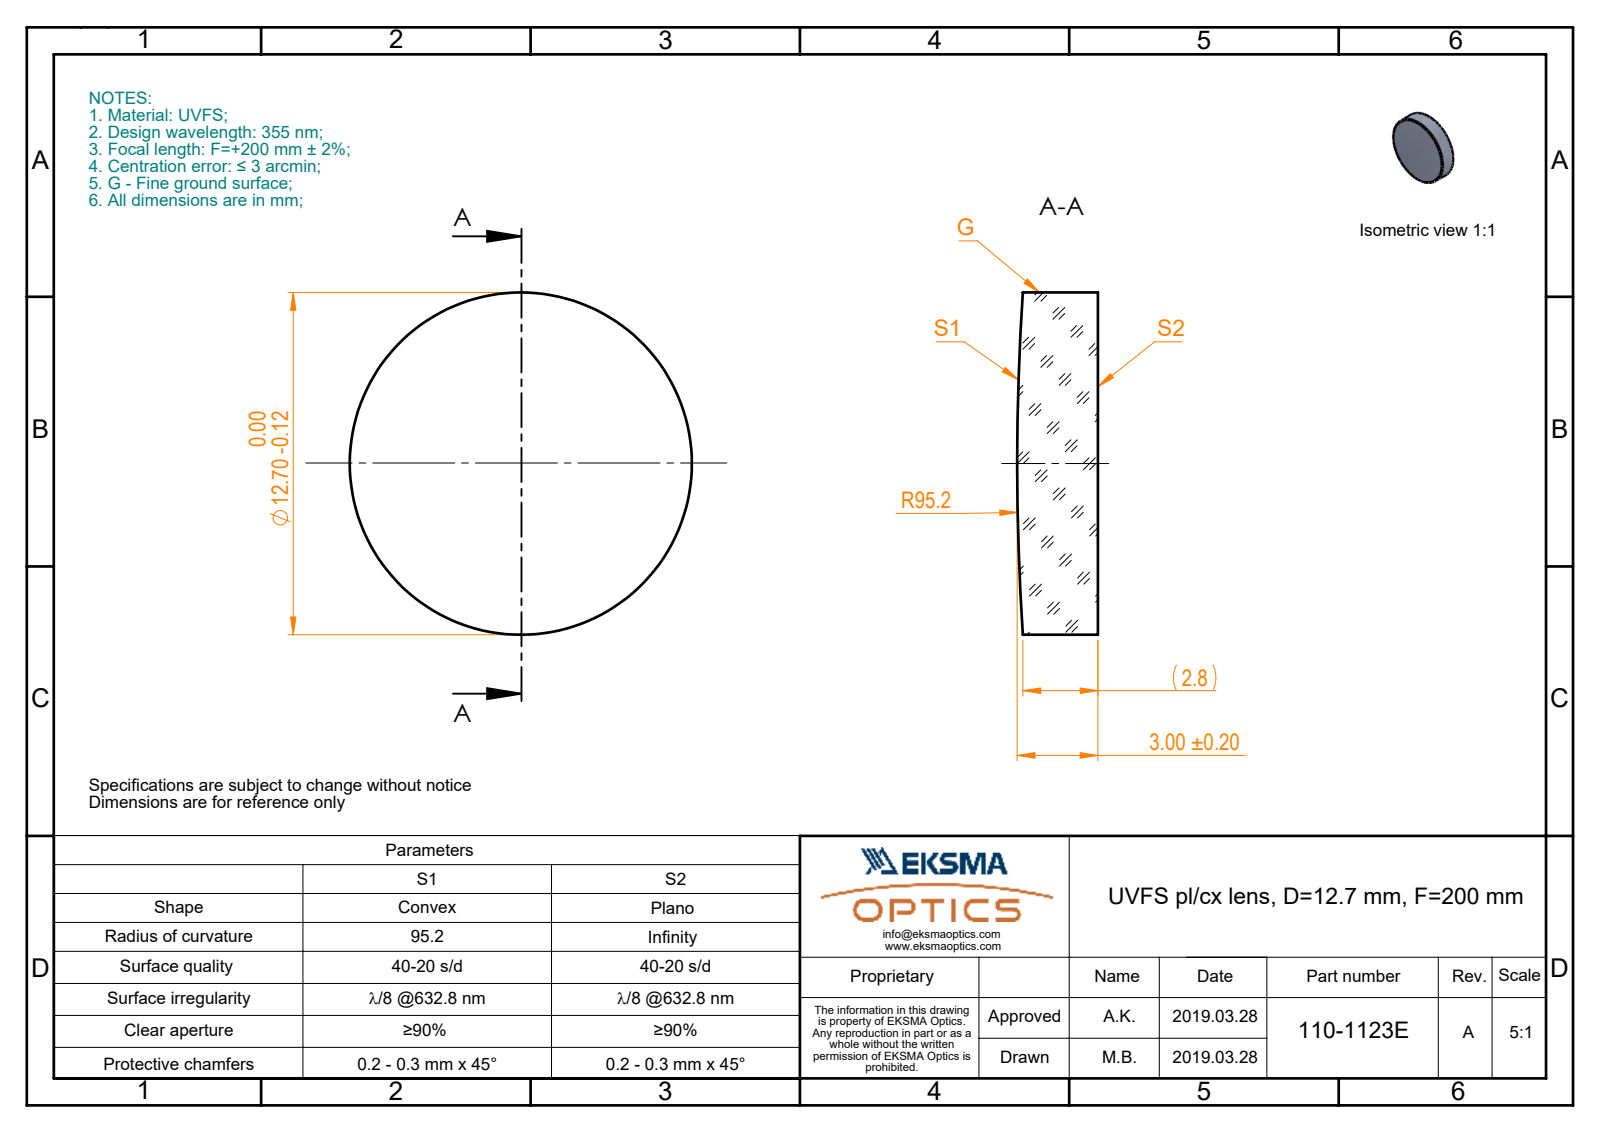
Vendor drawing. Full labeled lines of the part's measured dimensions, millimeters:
Part name (STEP PRODUCT): 110-1123E UVFS pl-cx 12.7 F200
STEP written by: SolidWorks 2017 (CONFIG_CONTROL_DESIGN)
Units: millimetres
Bodies: 1 solid, 5 faces (1 planar, 2 cylindrical, 2 other)
Overall size (bounding box): 12.7 × 12.7 × 3
Volume: 367 mm³ · Surface area: 365 mm²
Round bosses / shafts (diameter × count): ⌀12.7 ×1
